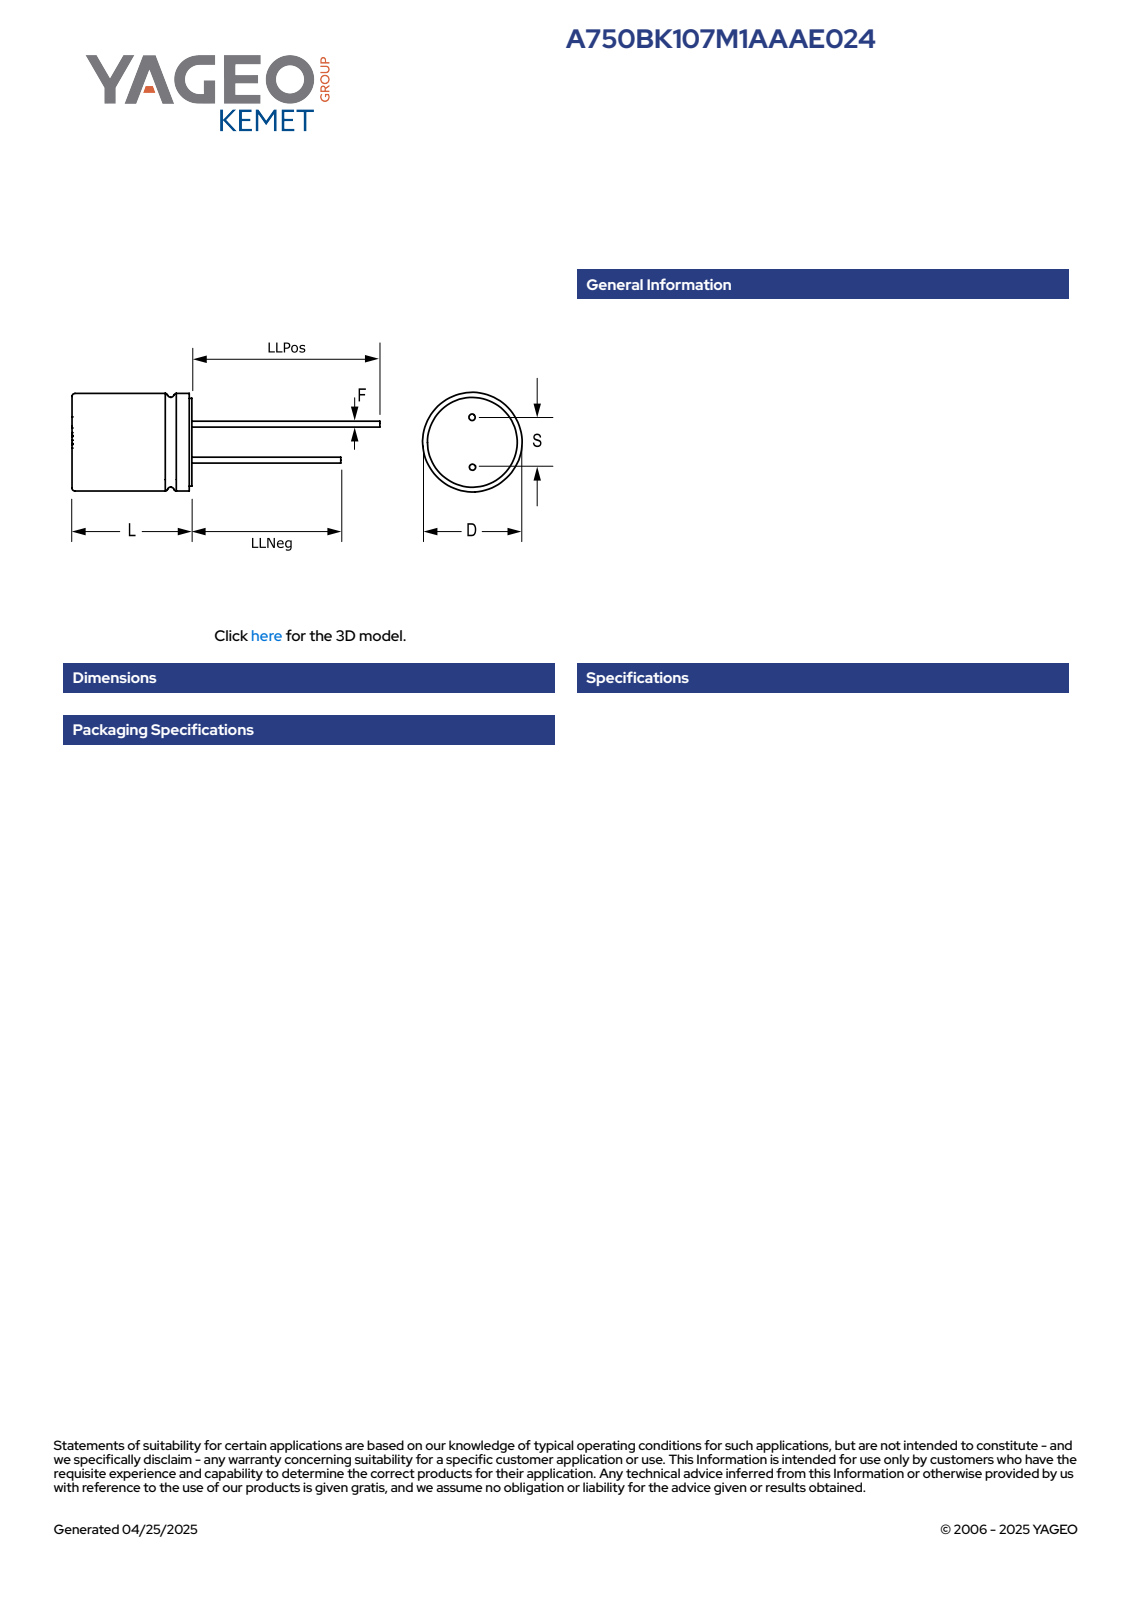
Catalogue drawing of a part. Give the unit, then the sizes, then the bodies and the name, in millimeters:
Units: millimetres
Overall size (bounding box): 28 × 5.5 × 5.5
Round bosses / shafts (diameter × count): ⌀0.55 ×2, ⌀5.5 ×1
Main face-to-face distances: 9, 9.01, 24.01, 28.01, 24, 28, 15, 19, 4, 0.6
Volume: 220 mm³ · Surface area: 267 mm²
Bodies: 4 solids, 75 faces (61 planar, 8 cylindrical, 6 other)
Part name (STEP PRODUCT): CAR_KP_5X8_D5.5L9S2F0.55
STEP written by: SolidWorks 2014 (AUTOMOTIVE_DESIGN)
